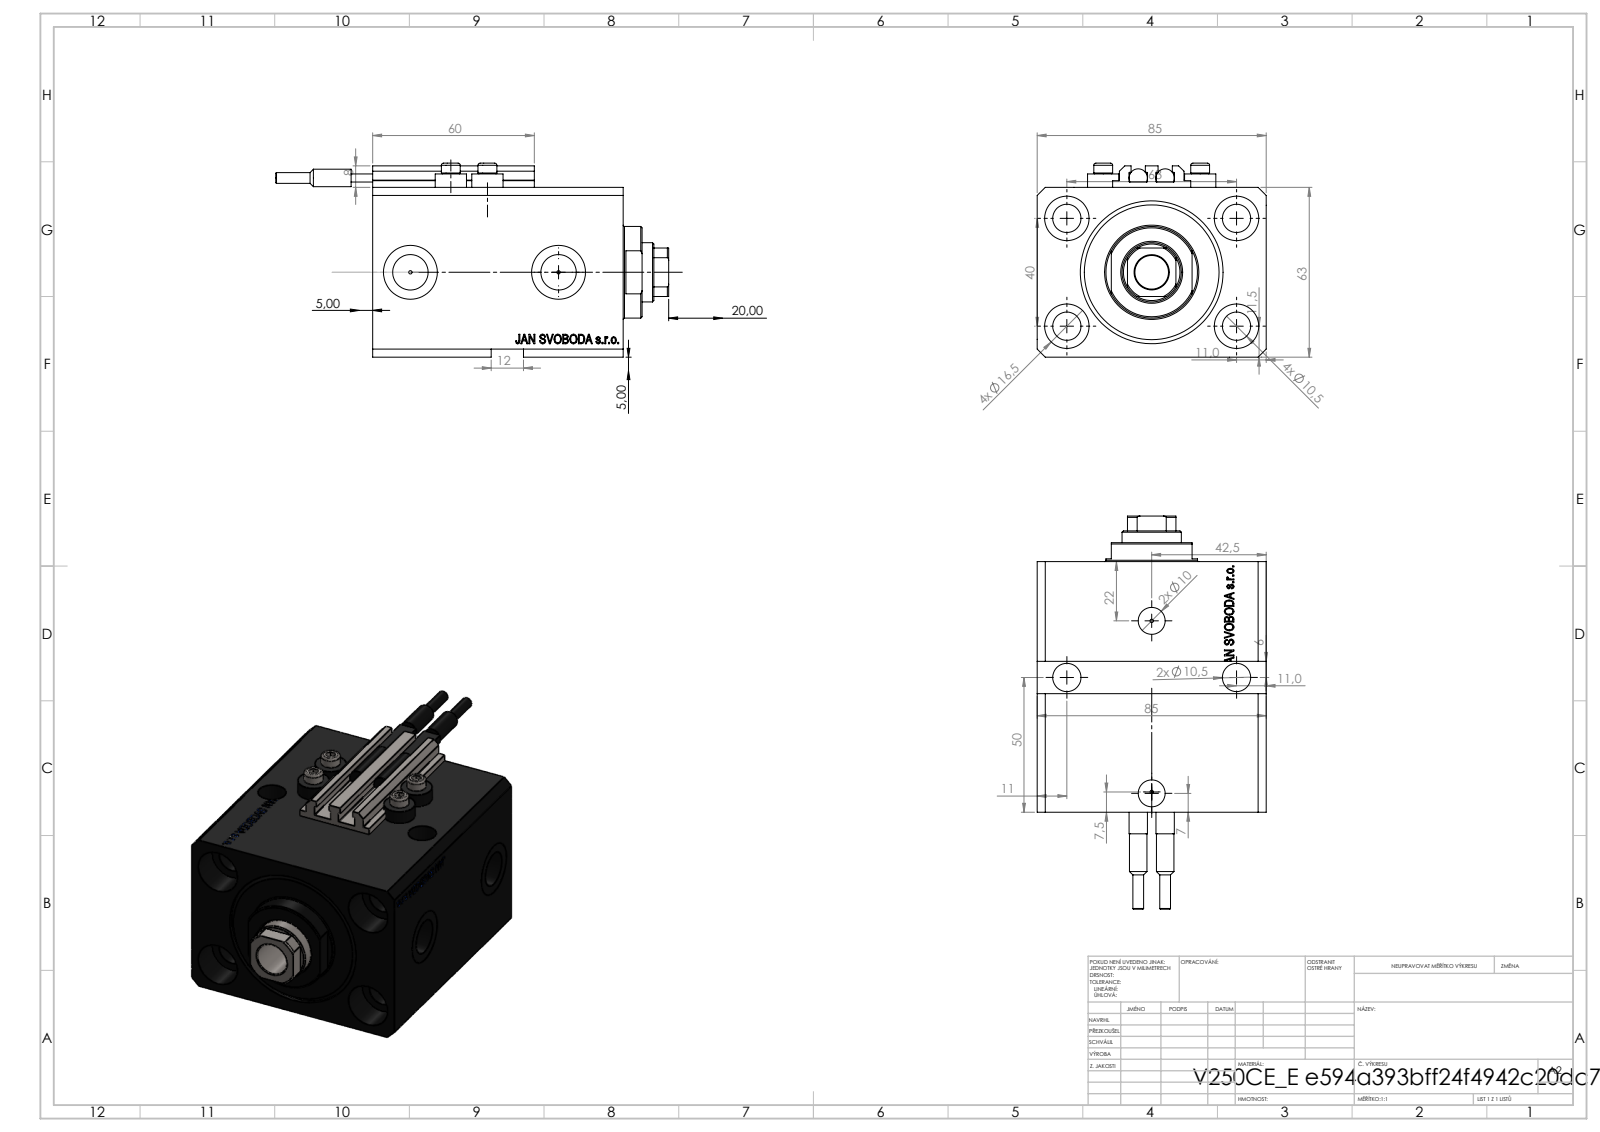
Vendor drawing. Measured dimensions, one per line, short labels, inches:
name: V250CE_E_Body; ALLEN BOLT V250CE; V250CE_VC_E; SWITCH_V250CE (+1 more)
written by: SolidWorks 2019 (CONFIG_CONTROL_DESIGN)
unit: in
bodies: 10 solids, 1155 faces (571 planar, 150 cylindrical, 434 other)
size: 5.744 × 3.346 × 2.835
volume: 26.68 in³; area: 157.8 in²
holes: 6× ⌀0.413, 4× ⌀0.049, 4× ⌀0.157, 4× ⌀0.65, 2× ⌀0.394, 2× ⌀0.518, 2× ⌀0.787, 1× ⌀0.492, 1× ⌀0.866, 1× ⌀1.575, 1× ⌀2.087
bosses: 4× ⌀0.457, 4× ⌀0.276, 2× ⌀0.268, 2× ⌀0.256, 2× ⌀0.157, 1× ⌀1.339
rounds: 10× R0.008, 1× R0.413
face distances: 2.48, 3.346, 3.661, 2.594, 2.146, 1.067, 0.449, 3.213, 0.118, 2.559
hole spacings: 1.469, 2.48, 0.535, 0.606, 0.983, 1.103, 1.119, 1.324
